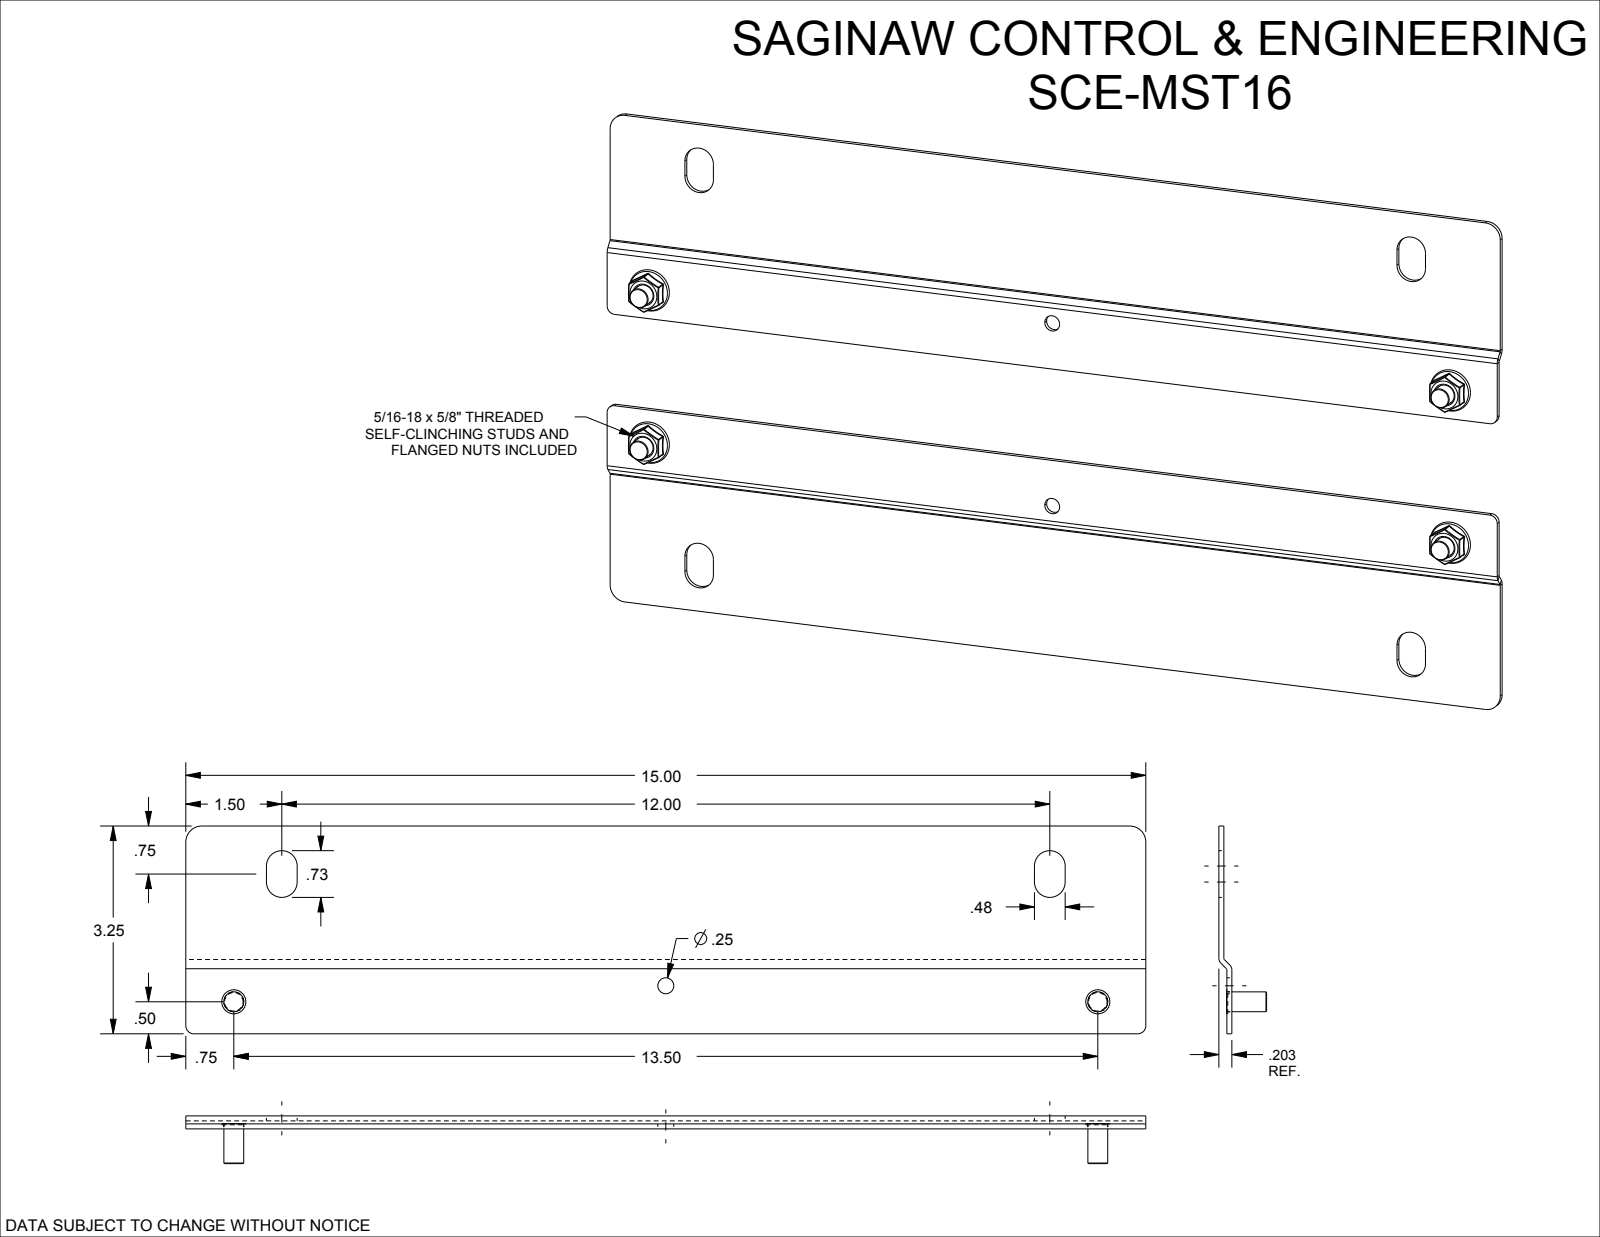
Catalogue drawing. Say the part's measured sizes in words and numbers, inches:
The part is named "SCE-MST16". Its 3-D file was written by "SolidWorks 2019 (AUTOMOTIVE_DESIGN)". It is 10 solids with 258 faces: 72 planar, 66 cylindrical and 120 other. Overall it measures 15 by 7.99 by 0.746 inches. Its volume is 7.965 cubic inches and its surface area 209 square inches. Round holes: 4 of diameter 0.312, 2 of diameter 0.25. Round bosses or shafts: 4 of diameter 0.376, 4 of diameter 0.31. Partial cylindrical surfaces (rounded edges, fillets, slot ends): 24 of radius 0.01, 8 of radius 0.24, 4 of radius 0.023, 4 of radius 0.101, 4 of radius 0.125, 4 of radius 0.25. The main face-to-face distances are 0.078, 0.078, 0.125, 0.203, 0.047, 0.125, 3.245, 4.745, 1.5, 7.99. The hole center spacings are 6.755, 7.289, 2.5, 13.5, 13.73, 3.
